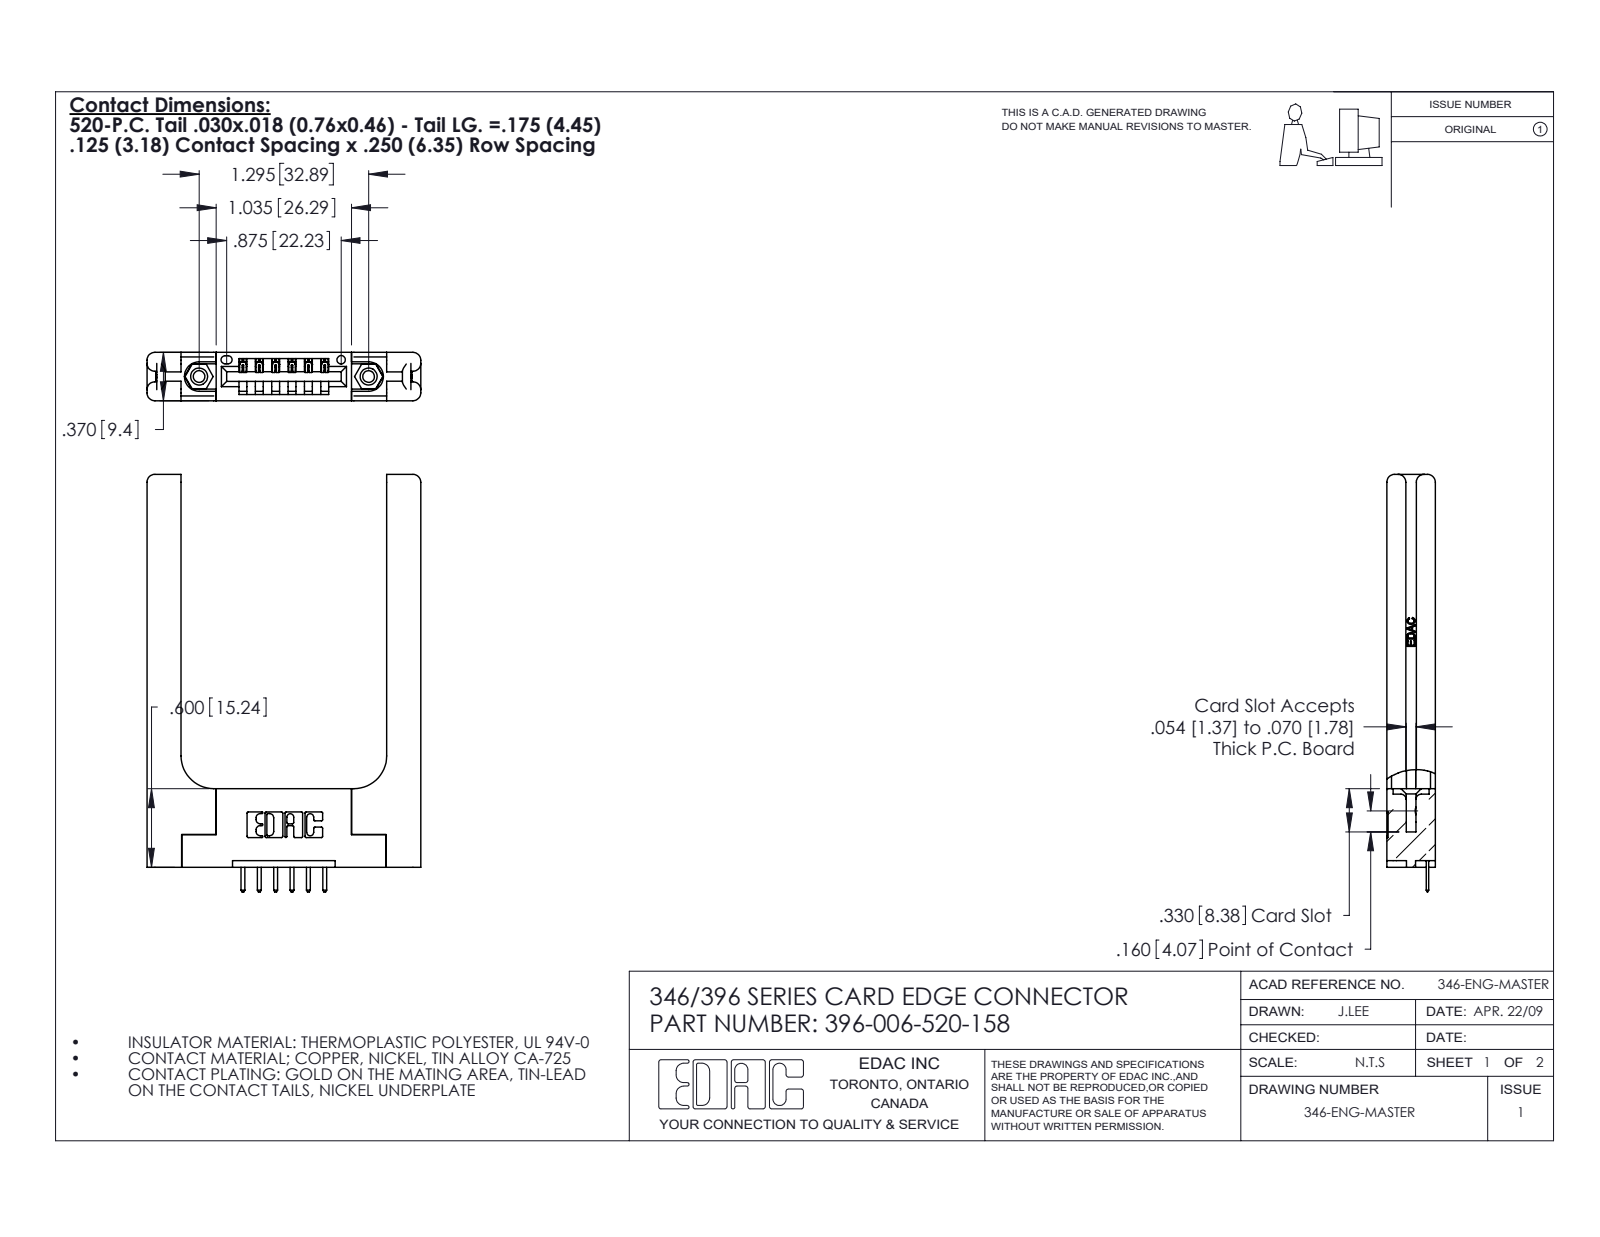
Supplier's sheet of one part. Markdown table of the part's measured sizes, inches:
| quantity | value |
| --- | --- |
| part name | 346-220-058_345-220-058; 345-250-001_345-250-001-102; 345-292-001_345-293-120; 396-006-520-158 (+1 more) |
| STEP written by | SolidWorks 2020 (CONFIG_CONTROL_DESIGN) |
| units | inches |
| bodies | 11 solids, 764 faces (490 planar, 214 cylindrical, 60 other) |
| overall size | 3.188 × 2.091 × 0.37 |
| volume | 0.752 in³ |
| surface area | 16.67 in² |
| round holes (diameter × count) | 0.089 × 2, 0.125 × 2, 0.156 × 2, 0.064 × 1 |
| round bosses / shafts (diameter × count) | 0.155 × 2 |
| partial cylindrical surfaces (radius × count) | 0.01 × 22, 0.06 × 16, 0.01 × 14, 0.006 × 12, 0.007 × 6, 0.031 × 6, 0.026 × 3, 0.03 × 2 |
| main face-to-face distances | 0.37, 0.15, 0.22, 0.25, 0.072, 1.571, 0.148, 0.071, 0.102, 0.048 |
| hole center spacings | 0.246, 1.092, 1.295 |
